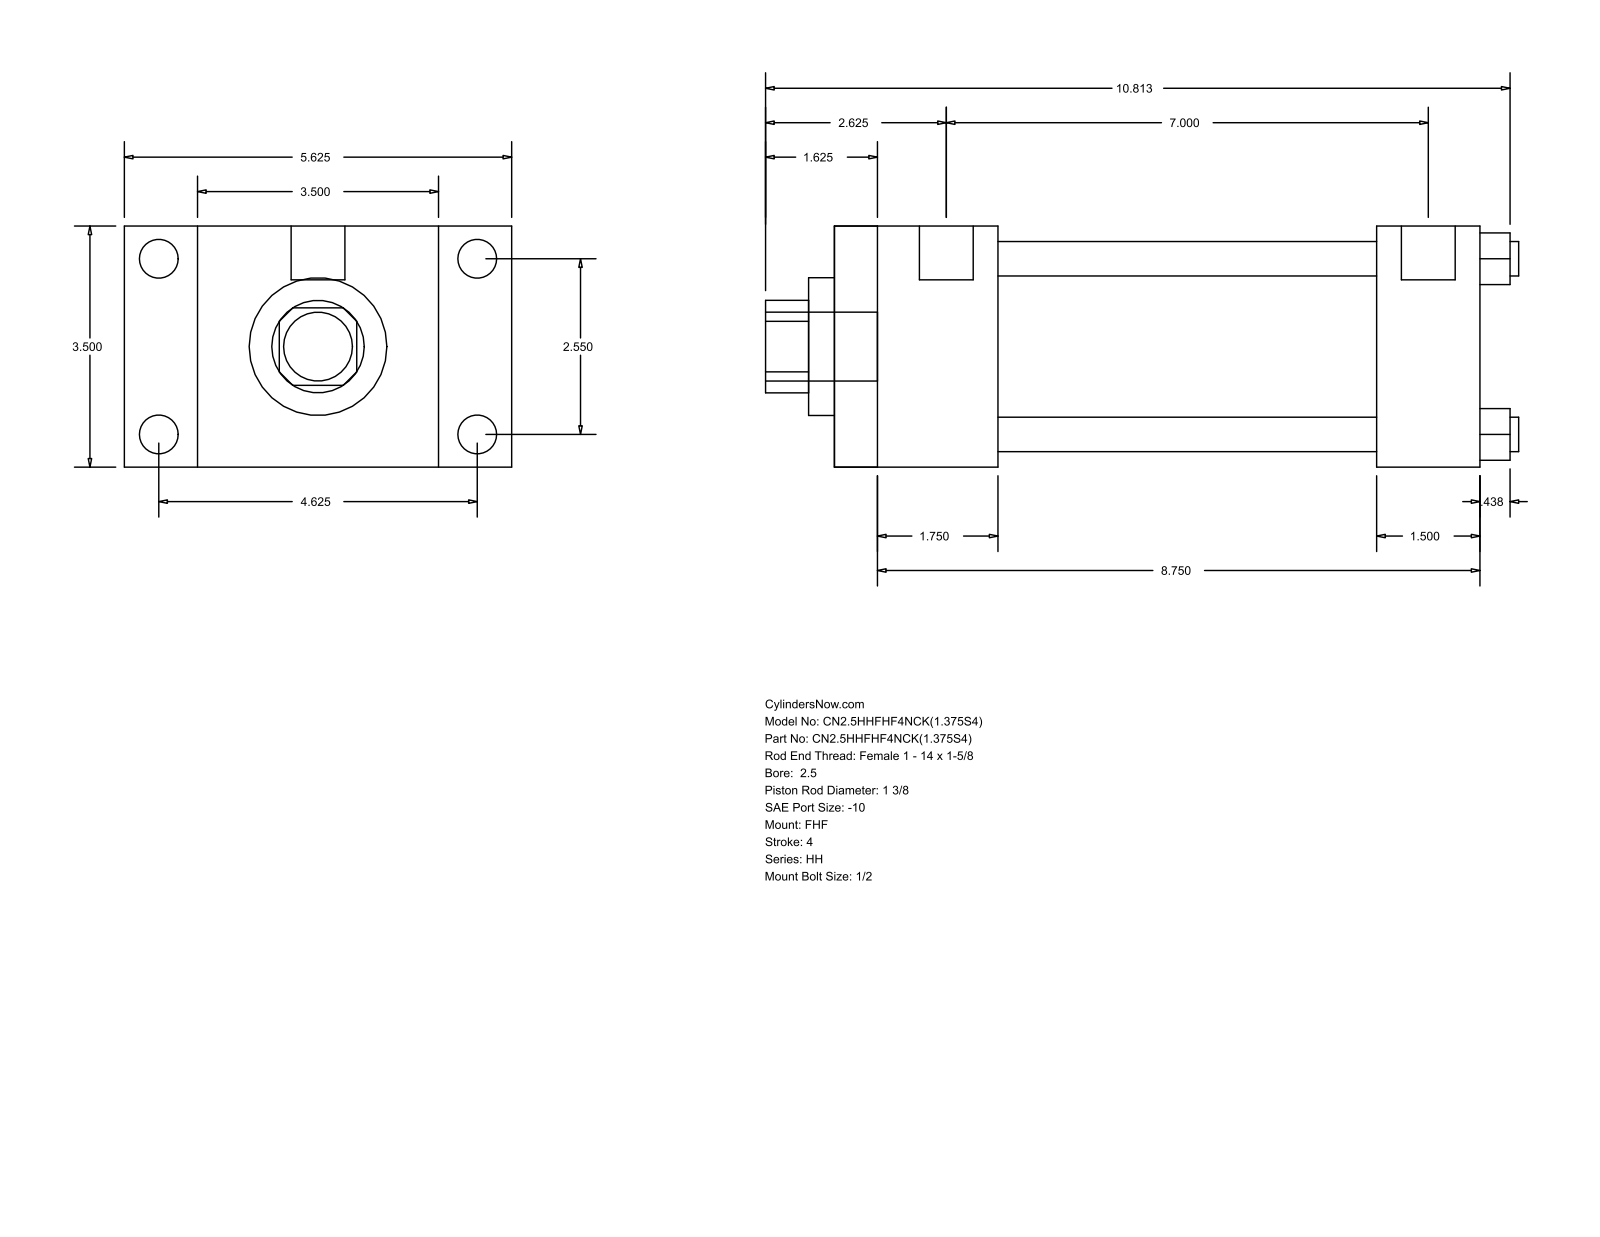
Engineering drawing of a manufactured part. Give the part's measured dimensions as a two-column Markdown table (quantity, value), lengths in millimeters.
| quantity | value |
| --- | --- |
| part name | HH_FHF__0250_1.375 |
| STEP written by | GSSL Pune (CONFIG_CONTROL_DESIGN) |
| units | millimeters |
| bodies | 0 solids, 88 faces (60 planar, 28 cylindrical, 0 other) |
| overall size | 277.81 × 142.88 × 88.9 |
| round holes (diameter × count) | 12.7 × 4, 34.92 × 1, 50.8 × 1, 73.03 × 1 |
| round bosses / shafts (diameter × count) | 14.3 × 4, 5.56 × 4, 19.84 × 2, 25.4 × 1 |
| partial cylindrical surfaces (radius × count) | 17.06 × 1 |
| main face-to-face distances | 88.9, 60.32, 26.99, 115.89, 238.12, 177.8, 142.88, 200.03, 139.71, 38.09 |
| hole center spacings | 45.79, 64.76, 91.58 |
